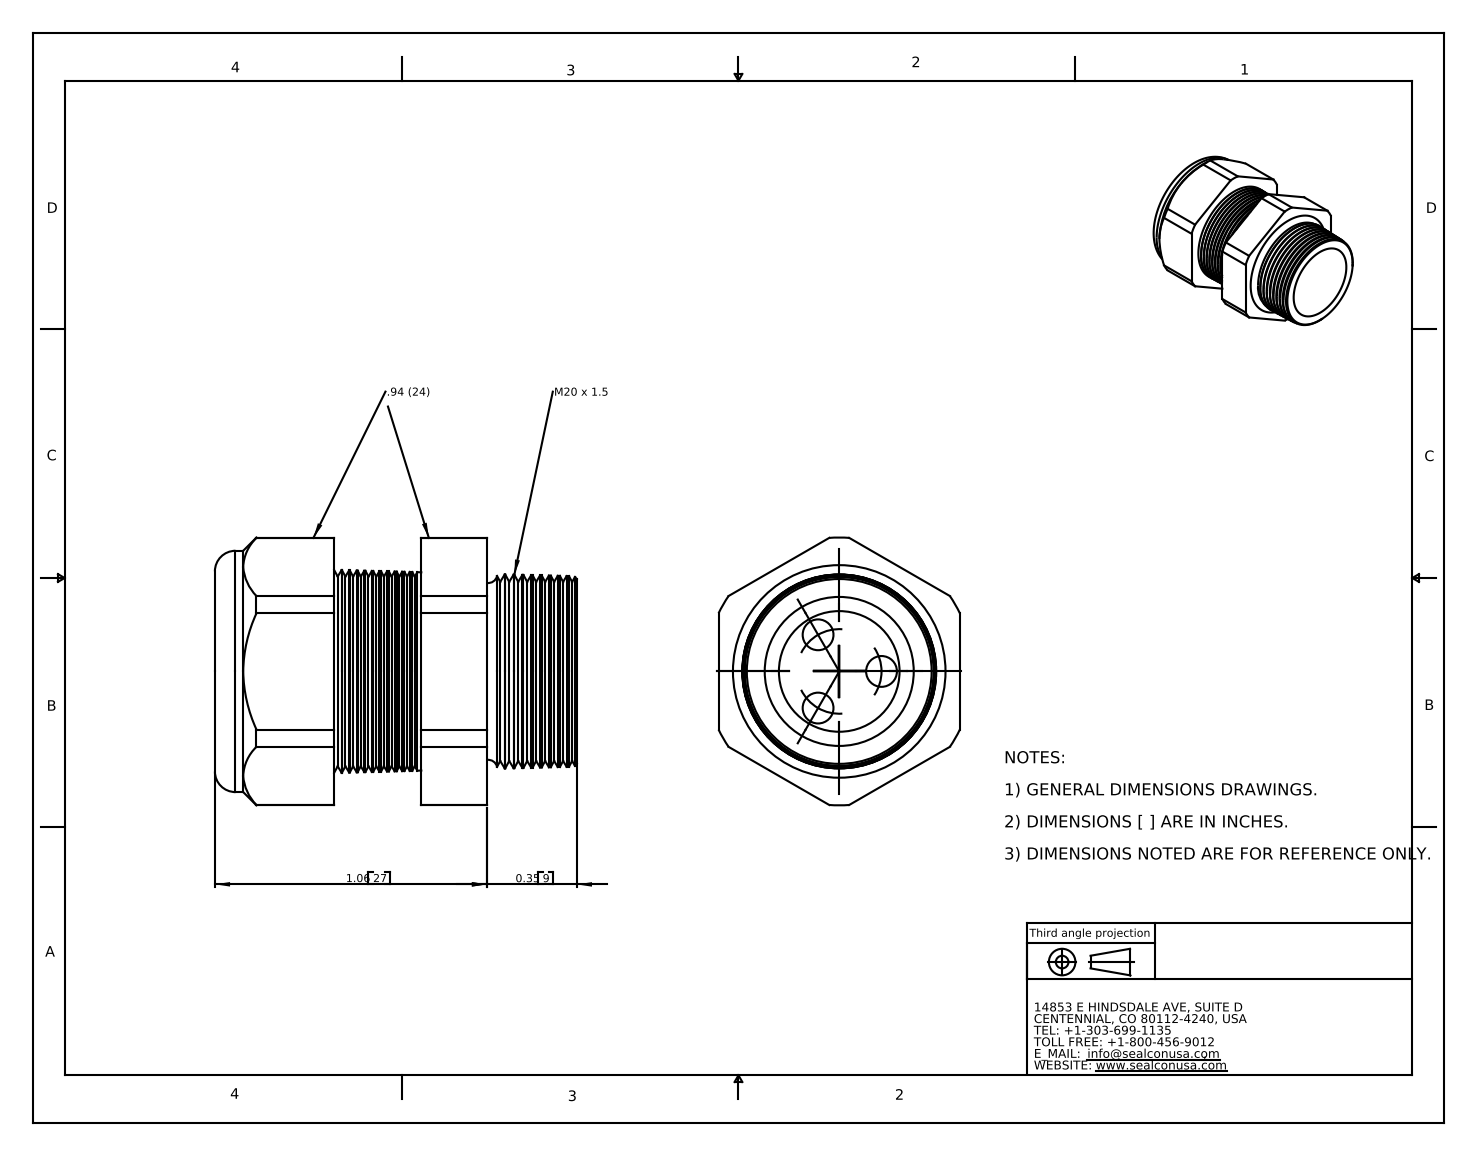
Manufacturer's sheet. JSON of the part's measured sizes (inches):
{"part_name": "CD20M5-GY", "step_written_by": "SolidWorks 2007 (CONFIG_CONTROL_DESIGN)", "units": "inches", "bodies": {"solids": 2, "faces": 180, "planar": 20, "cylindrical": 26, "other": 134}, "overall_size": [1.41, 1.043, 0.94], "volume_in3": 0.578, "surface_area_in2": 9.933, "round_holes": [[0.12, 3], [0.45, 1], [0.47, 1]], "round_bosses_or_shafts": [[0.94, 1]], "partial_cylinders_radius": [[0.522, 1]], "face_to_face_distances": [0.94, 0.804, 0.465, 0.34, 1.06, 0.596, 0.256, 1.41, 0.946, 0.606], "hole_center_spacings": [0.165, 0.285]}
